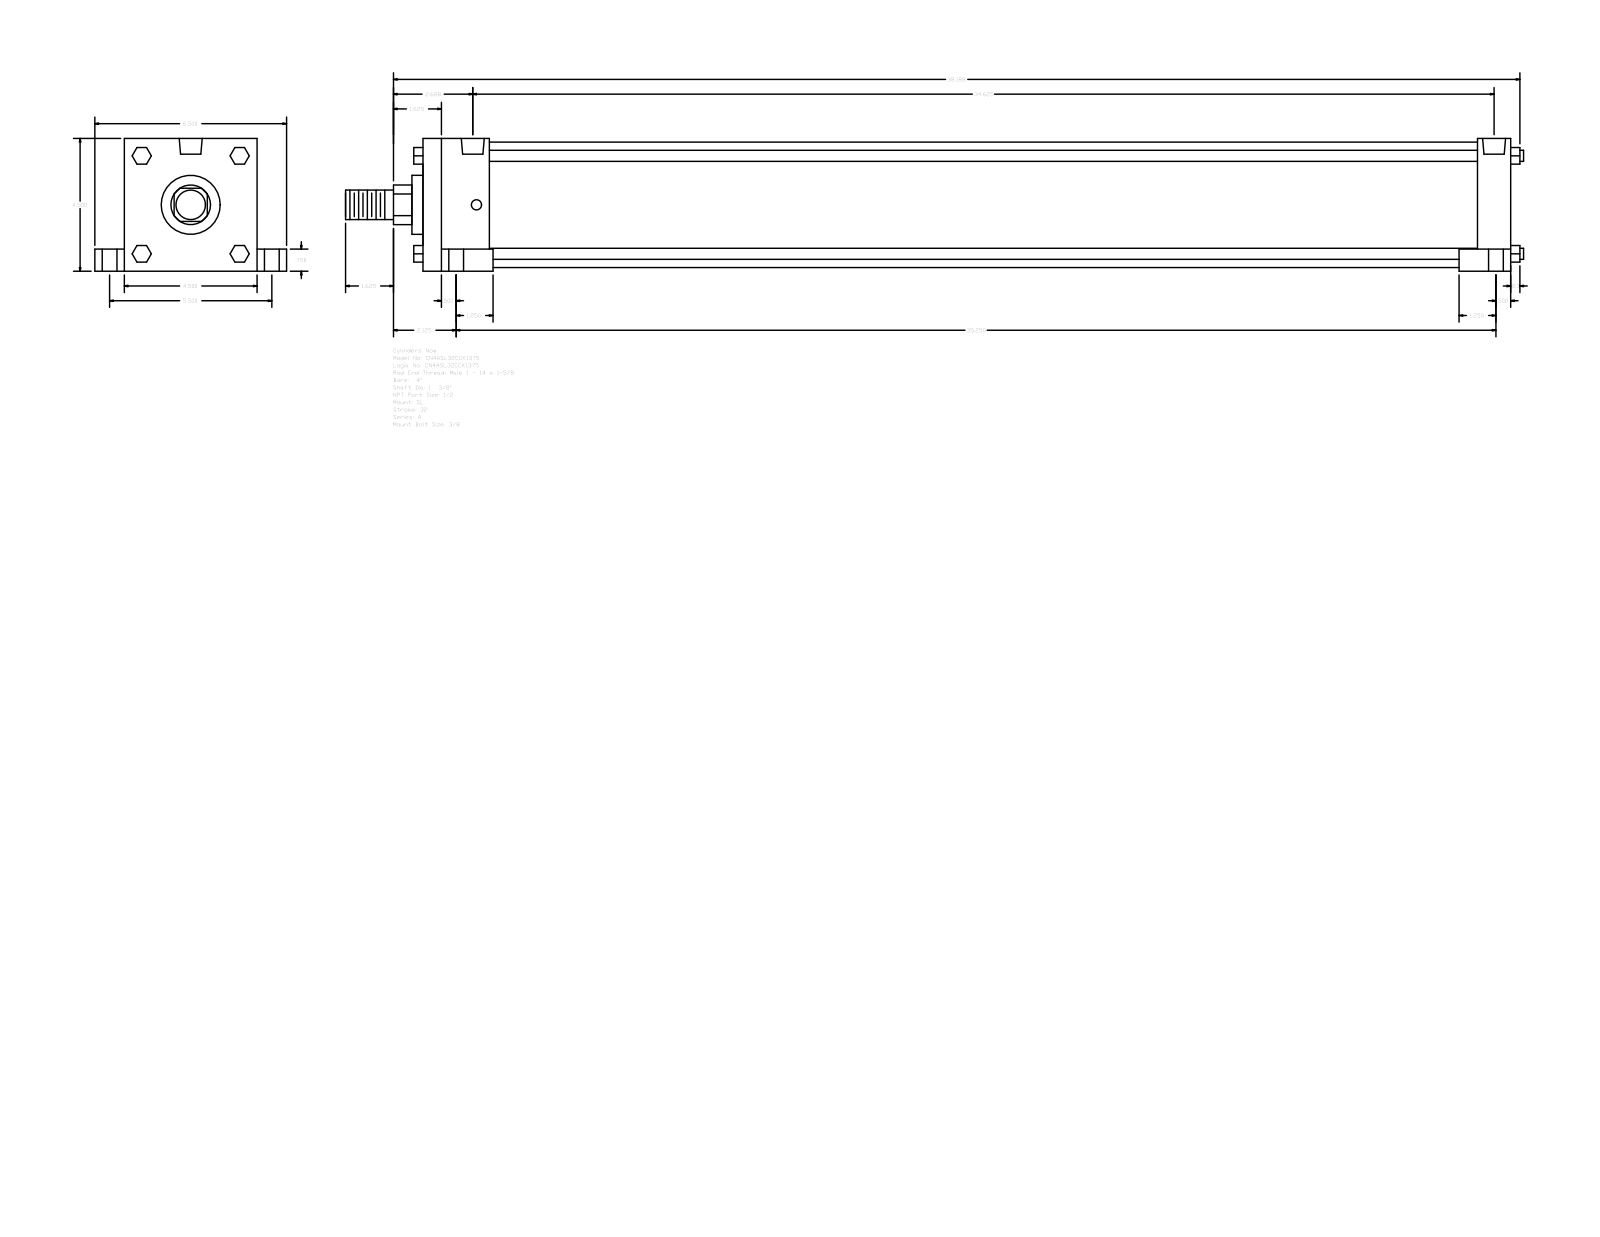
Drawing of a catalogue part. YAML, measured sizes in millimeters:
part_name: "A_SL__0400_1.375"
step_written_by: "GSSL Pune (CONFIG_CONTROL_DESIGN)"
units: millimeters
bodies: {solids: 0, faces: 150, planar: 114, cylindrical: 36, other: 0}
overall_size: [1014.41, 165.1, 114.3]
round_holes:
  - {diameter: 8.73, count: 4}
  - {diameter: 12.7, count: 4}
  - {diameter: 19.05, count: 4}
  - {diameter: 19.77, count: 2}
round_bosses_or_shafts:
  - {diameter: 9.53, count: 4}
  - {diameter: 107.95, count: 1}
  - {diameter: 50.8, count: 1}
  - {diameter: 34.92, count: 1}
  - {diameter: 25.4, count: 1}
partial_cylinders:
  - {radius: 17.06, count: 1}
face_to_face_distances: [114.3, 936.62, 57.15, 28.57, 25.4, 879.47, 908.05, 850.9, 139.7, 19.05]
hole_center_spacings: [3.18, 69.87, 70.01, 71.29, 72, 139.7, 873.12, 876.3]
